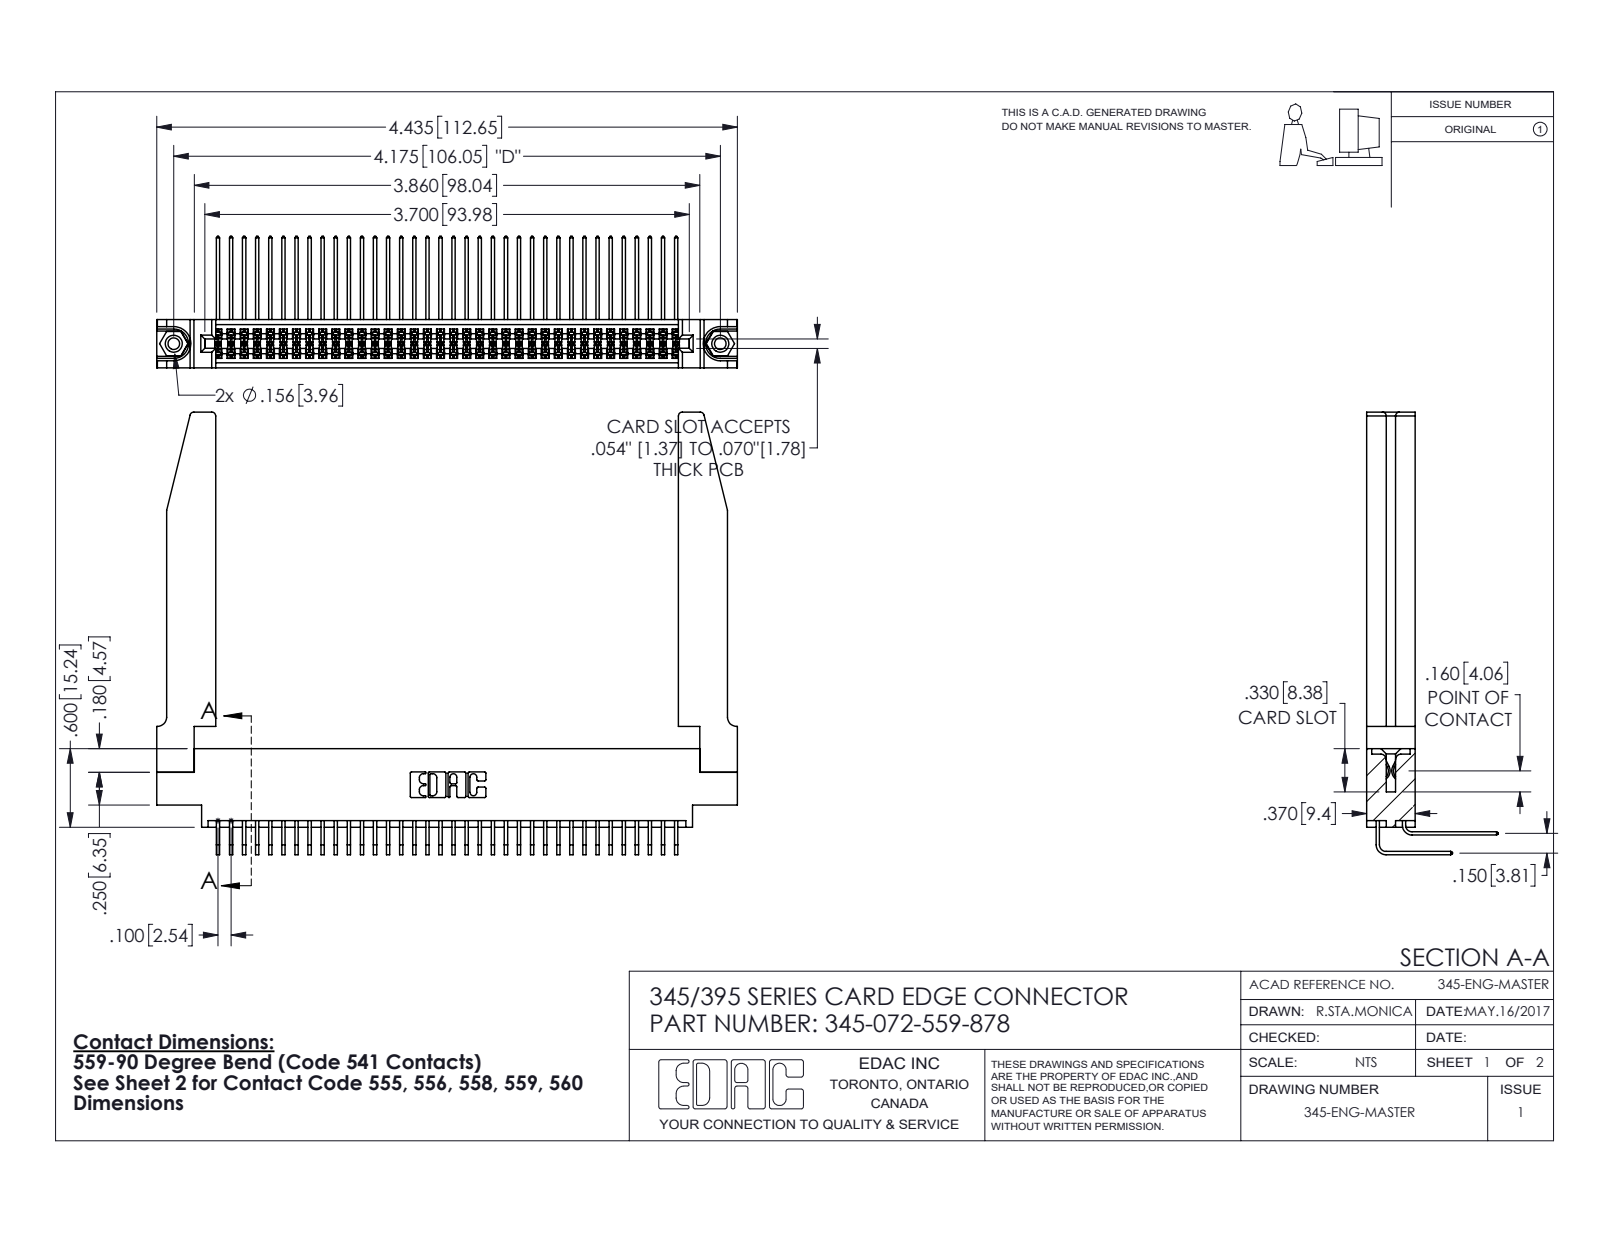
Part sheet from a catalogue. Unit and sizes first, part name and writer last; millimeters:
Units: millimetres
Overall size (bounding box): 112.7 × 85.8 × 25.5
Round holes (diameter × count): ⌀2.3 ×2, ⌀3.2 ×2, ⌀4 ×2, ⌀1.6 ×1
Round bosses / shafts (diameter × count): ⌀3.9 ×2
Partial cylindrical surfaces — rounded edges, fillets, slot ends (radius × count): R0.2 ×143, R0.3 ×22, R0.8 ×8, R0.2 ×6, R0.8 ×6, R0.7 ×3, R0.4 ×2, R0.5 ×2
Main face-to-face distances: 9.4, 1.8, 7.6, 5.1, 2.5, 6.9, 0.6, 5.7, 3.8, 4.4
Hole centre spacings: 6.9, 100.1, 106
Volume: 18 960 mm³ · Surface area: 25 360 mm²
Bodies: 77 solids, 4108 faces (2746 planar, 1310 cylindrical, 52 other)
Part name (STEP PRODUCT): 345-220-078_345-220-078; 345-250-001_345-250-001-102; 345 Part_0.170 Offset - 0.156 Dia-TH; 345-292-001_558 559 Tail - 1 (+2 more)
STEP written by: SolidWorks 2016 (CONFIG_CONTROL_DESIGN)
